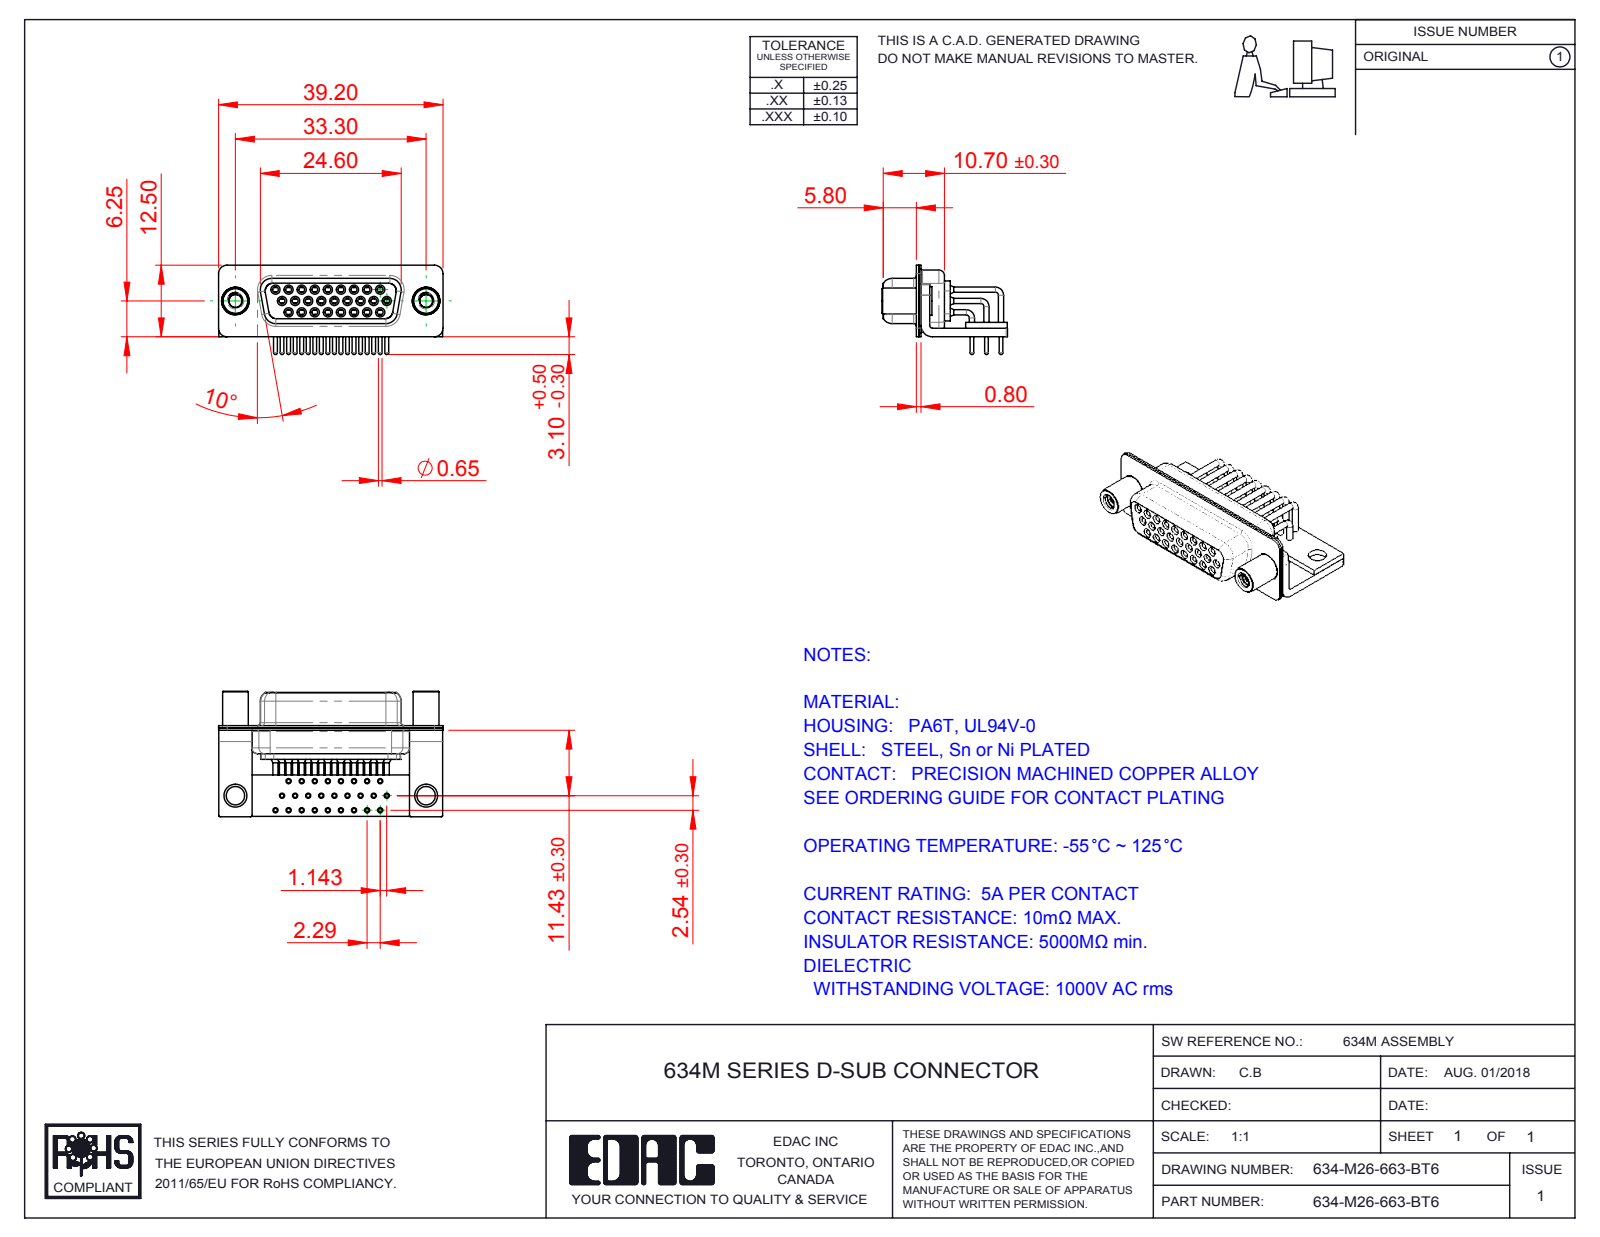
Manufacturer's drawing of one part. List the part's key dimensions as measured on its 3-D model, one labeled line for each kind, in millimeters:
Part name (STEP PRODUCT): 634M Stabilizer Board_26 Contacts; 634M 4-40 Threaded Standoff; 634M Stabilizer Bracket; 634M Housing_26 Contacts (+6 more)
STEP written by: SolidWorks 2016 (CONFIG_CONTROL_DESIGN)
Units: millimetres
Bodies: 34 solids, 1809 faces (485 planar, 851 cylindrical, 473 other)
Overall size (bounding box): 39.2 × 21.9 × 15.6
Volume: 3 190 mm³ · Surface area: 10 090 mm²
Round holes (diameter × count): ⌀0.9 ×26, ⌀1 ×26, ⌀1.1 ×26, ⌀1.7 ×26, ⌀1.8 ×26, ⌀2 ×26, ⌀2.26 ×2, ⌀3.2 ×2, ⌀4 ×2, ⌀4.8 ×2
Round bosses / shafts (diameter × count): ⌀0.9 ×27, ⌀1.6 ×26, ⌀1.5 ×26, ⌀0.65 ×26, ⌀5 ×2, ⌀4.9 ×2, ⌀4.5 ×2, ⌀2 ×1
Partial cylindrical surfaces — rounded edges, fillets, slot ends (radius × count): R0.25 ×16, R1.5 ×16, R2 ×13, R1.35 ×8, R1.6 ×8, R0.5 ×5, R0.6 ×4, R0.65 ×4
Main face-to-face distances: 0.4, 2.3, 1.9, 0.8, 1, 1.5, 9.35, 8.5, 1.45, 8.95
Hole centre spacings: 4.57, 2.29, 2.28, 3.96, 6.05, 6.86, 4.27, 2.78
